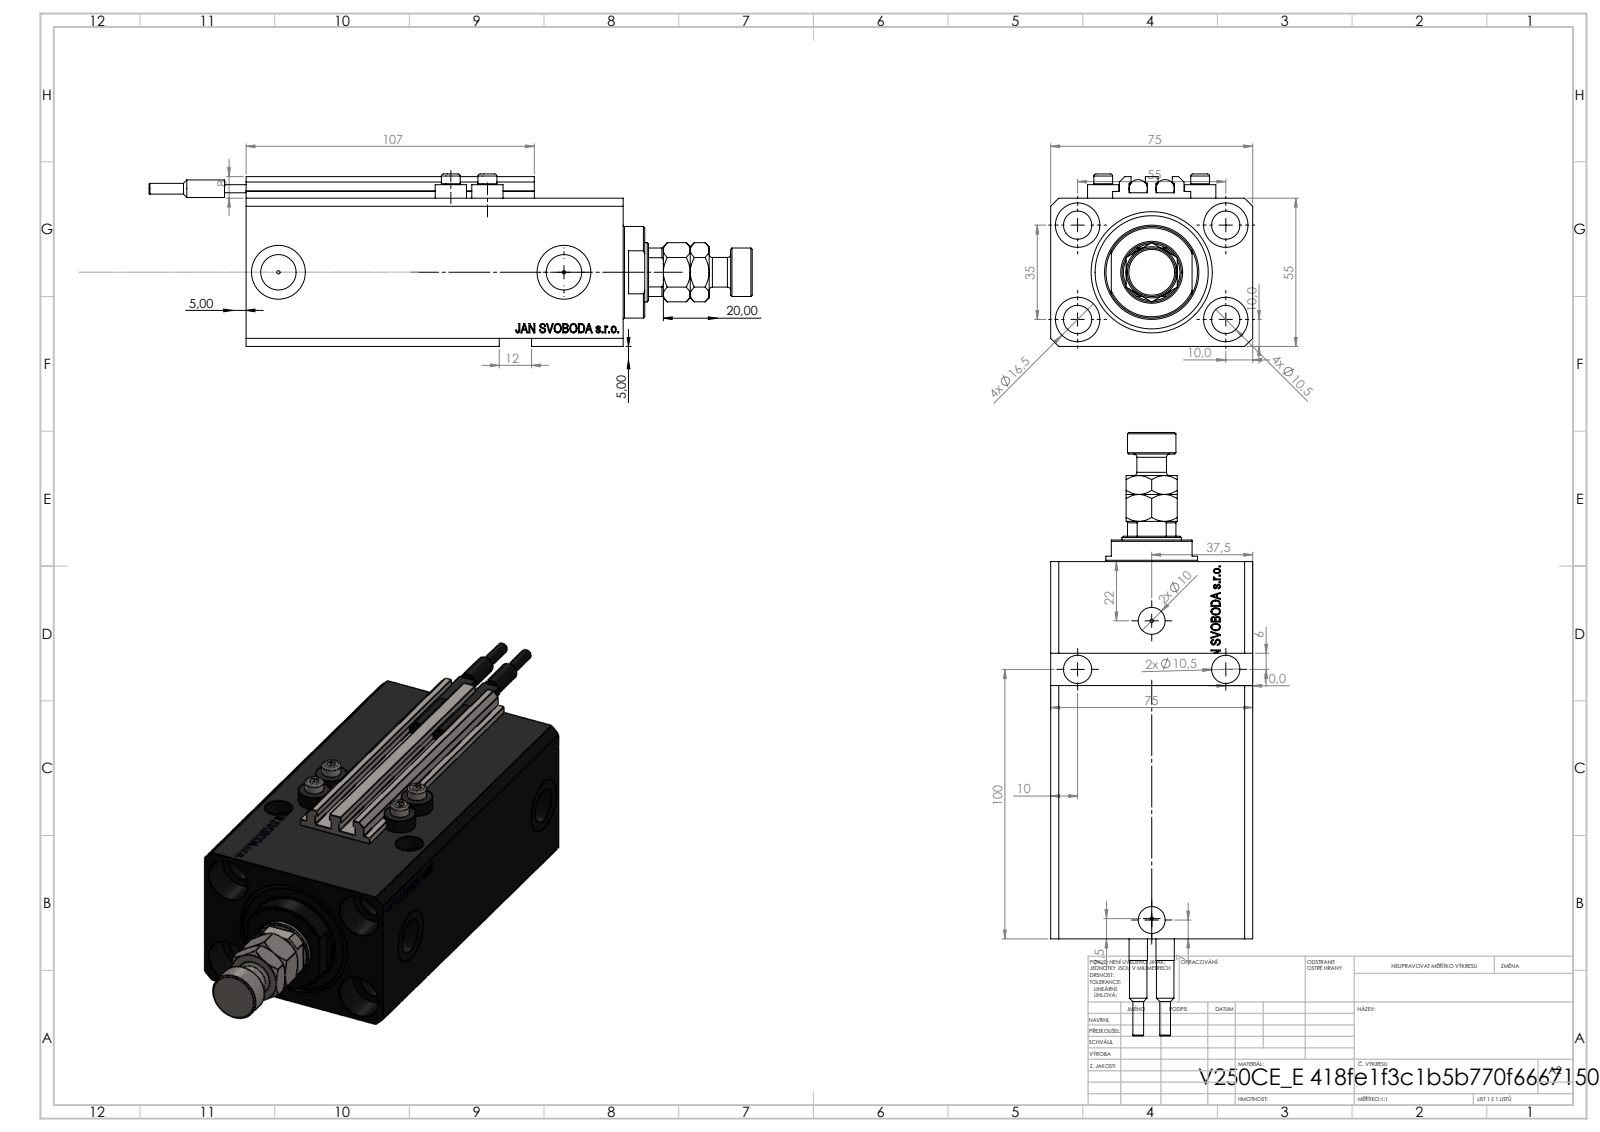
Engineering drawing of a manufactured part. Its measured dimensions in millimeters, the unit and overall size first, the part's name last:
Units: millimetres
Overall size (bounding box): 224 × 75 × 64
Round holes (diameter × count): ⌀10.5 ×9, ⌀1.25 ×4, ⌀4 ×4, ⌀16.5 ×4, ⌀10 ×2, ⌀13.16 ×2, ⌀20 ×2, ⌀22 ×1, ⌀32 ×1, ⌀45 ×1
Round bosses / shafts (diameter × count): ⌀11.6 ×4, ⌀7 ×4, ⌀6.8 ×2, ⌀6.5 ×2, ⌀4 ×2, ⌀34 ×1, ⌀18 ×1, ⌀11 ×1
Partial cylindrical surfaces — rounded edges, fillets, slot ends (radius × count): R0.2 ×10, R10.5 ×1
Main face-to-face distances: 55, 75, 15, 57, 3, 140, 9.9, 125, 2.5, 2
Hole centre spacings: 32.6, 32.87, 55, 96.98, 13.6, 14.09, 25.81, 32.58
Volume: 493 240 mm³ · Surface area: 121 899 mm²
Bodies: 11 solids, 1204 faces (566 planar, 174 cylindrical, 464 other)
Part name (STEP PRODUCT): V250CE_VC_E; MFA; SWITCH_V250CE; ALLEN BOLT V250CE (+2 more)
STEP written by: SolidWorks 2019 (CONFIG_CONTROL_DESIGN)
